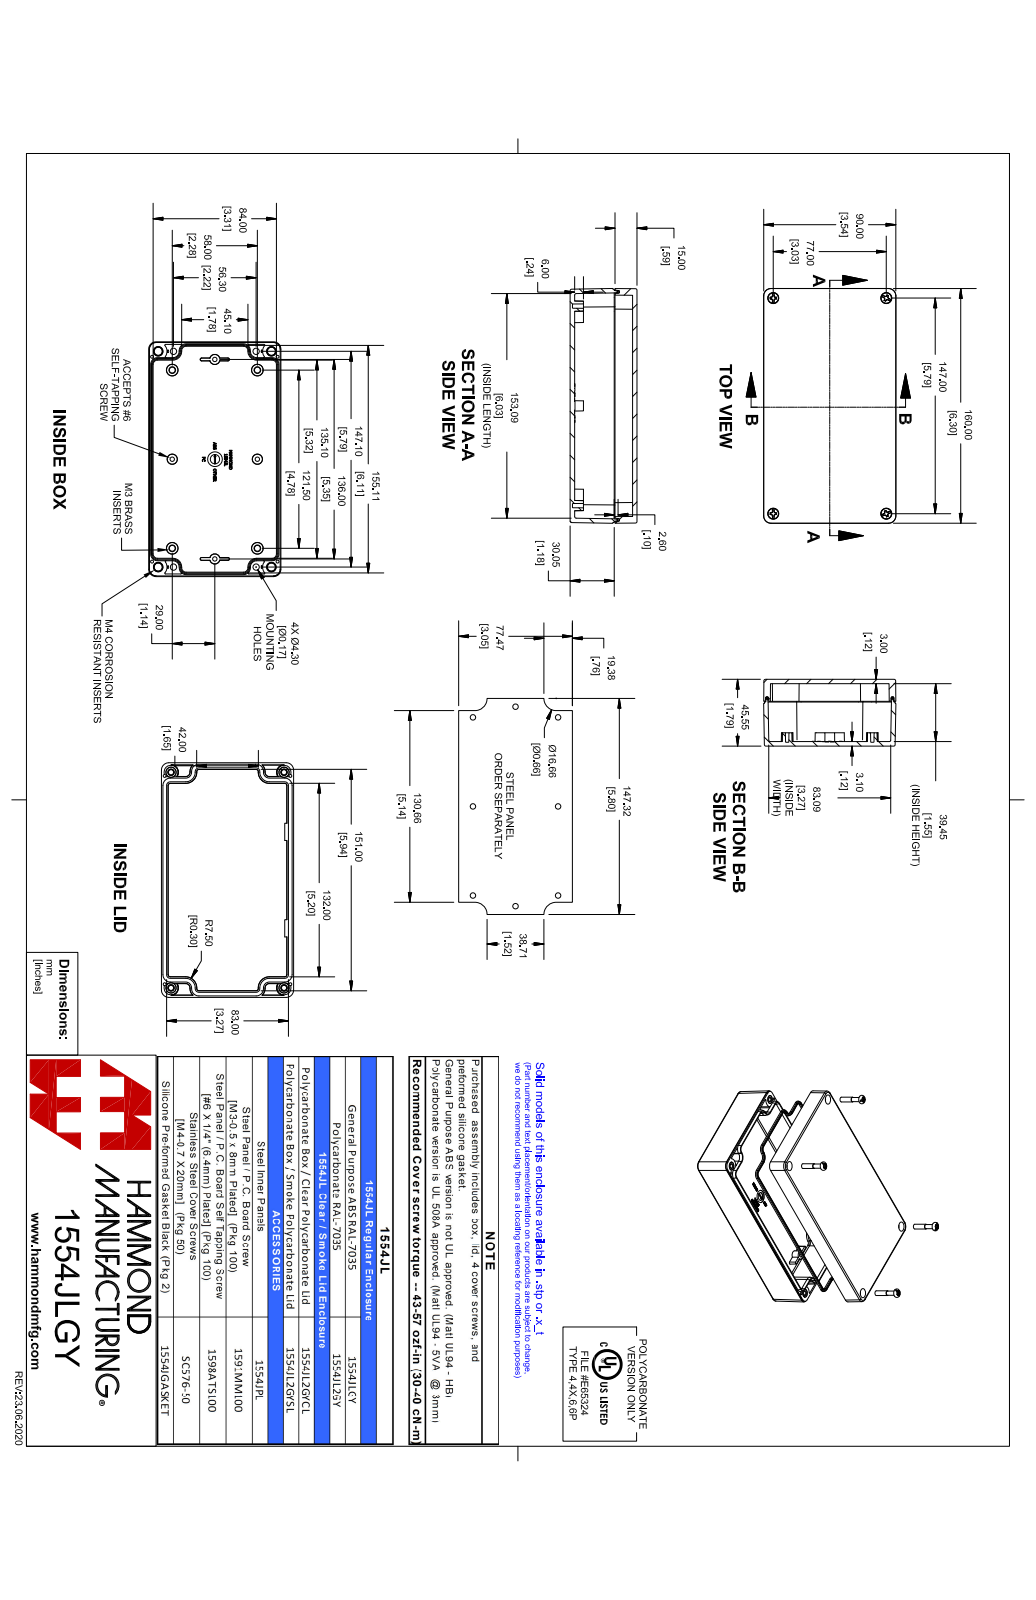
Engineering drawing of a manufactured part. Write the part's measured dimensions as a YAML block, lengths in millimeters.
part_name: "1554JLGY"
step_written_by: "SolidWorks 2021 (AUTOMOTIVE_DESIGN)"
units: millimeters
bodies: {solids: 15, faces: 1638, planar: 366, cylindrical: 395, other: 877}
overall_size: [160.1, 90.1, 45.5]
volume: 165200
surface_area: 117500
round_holes:
  - {diameter: 2, count: 4}
  - {diameter: 2.5, count: 4}
  - {diameter: 3.3, count: 4}
  - {diameter: 3.5, count: 4}
  - {diameter: 4.6, count: 4}
  - {diameter: 7, count: 4}
round_bosses_or_shafts:
  - {diameter: 6.4, count: 4}
  - {diameter: 5.5, count: 4}
  - {diameter: 5.3, count: 4}
  - {diameter: 4.8, count: 4}
  - {diameter: 3.9, count: 4}
  - {diameter: 3.9, count: 4}
  - {diameter: 3.8, count: 4}
  - {diameter: 3.4, count: 4}
partial_cylinders:
  - {radius: 1, count: 18}
  - {radius: 0.5, count: 16}
  - {radius: 5, count: 8}
  - {radius: 0.8, count: 4}
  - {radius: 3, count: 4}
  - {radius: 4.7, count: 4}
face_to_face_distances: [45.5, 3, 42.5, 3.1, 39.4, 42.4, 3, 4.5, 1.5, 12]
hole_center_spacings: [5, 15.9, 17.2, 68.7, 72.6, 81.4, 132.5, 134.6]
